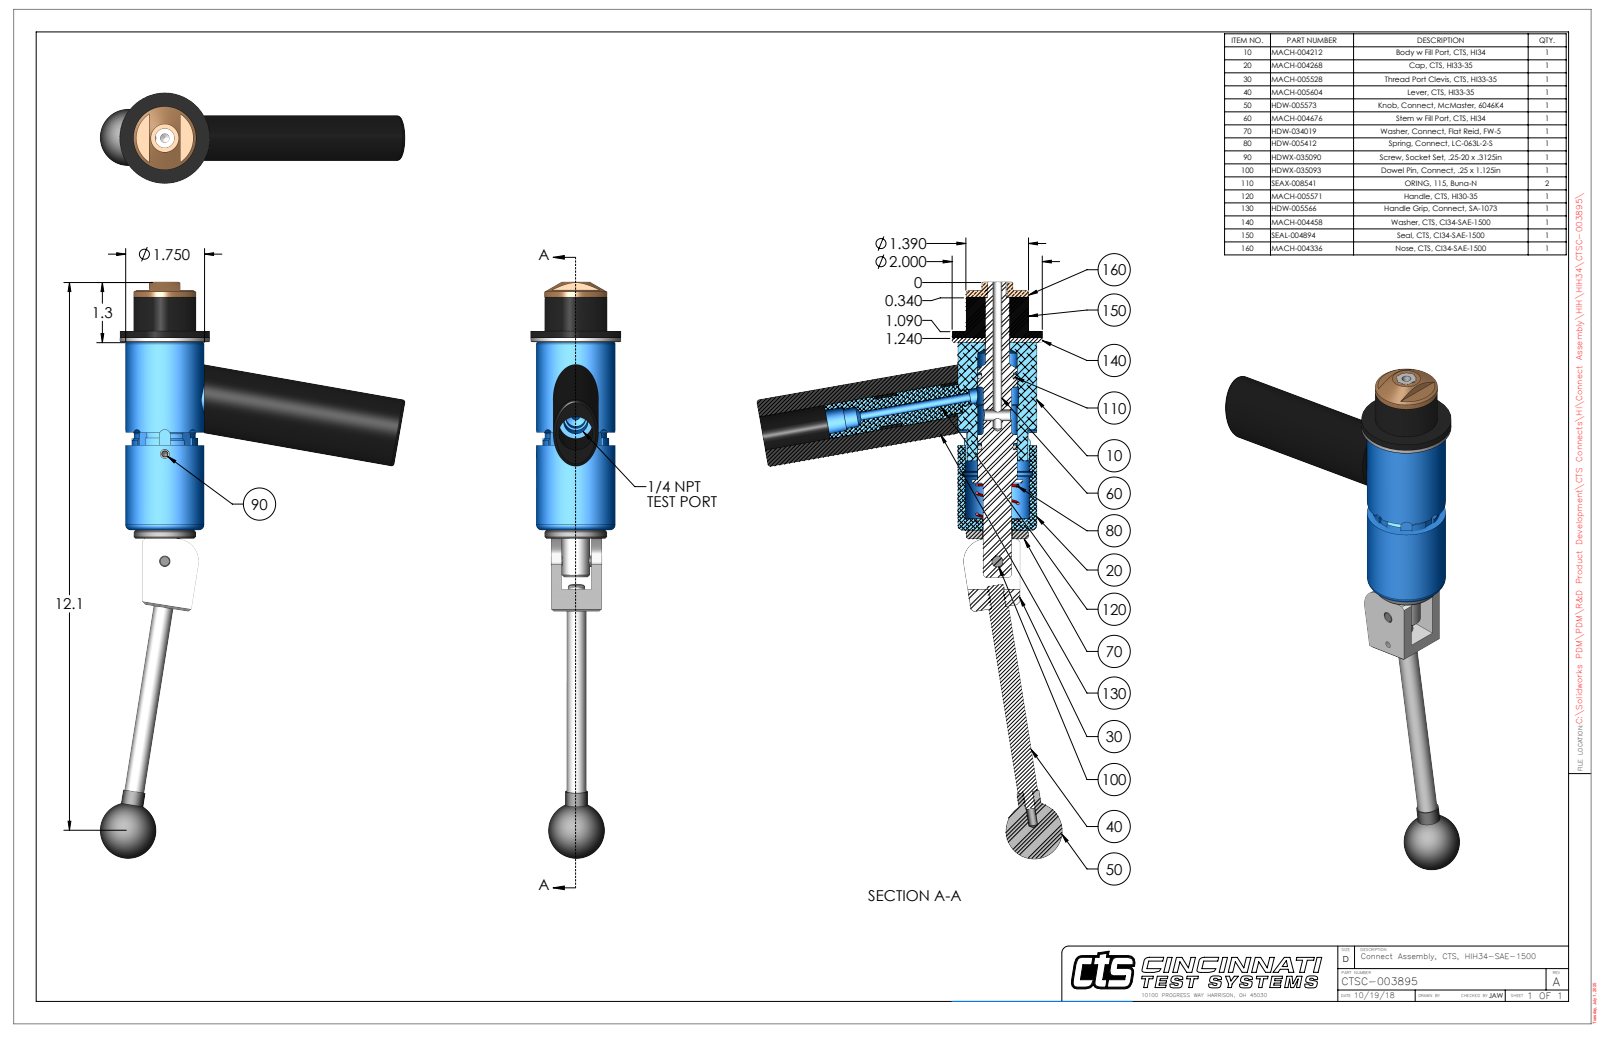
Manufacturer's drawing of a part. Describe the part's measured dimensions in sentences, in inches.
The part is named "CTSC-003895". Its 3-D file was written by "SolidWorks 2023 (AUTOMOTIVE_DESIGN)". It is 10 solids with 327 faces: 117 planar, 140 cylindrical and 70 other. Overall it measures 12.773 by 6.763 by 2 inches. Its volume is 19.51 cubic inches and its surface area 125.8 square inches. Round holes: 2 of diameter 0.201, 1 of diameter 0.15, 1 of diameter 0.187, 1 of diameter 0.204, 1 of diameter 0.249, 1 of diameter 0.25, 1 of diameter 0.251, 1 of diameter 0.313, 1 of diameter 0.422, 1 of diameter 0.438, 1 of diameter 0.53, 1 of diameter 0.541. Round bosses or shafts: 2 of diameter 0.5, 2 of diameter 0.44, 2 of diameter 0.25, 1 of diameter 2, 1 of diameter 1.75, 1 of diameter 1.39, 1 of diameter 1.38, 1 of diameter 0.75. Partial cylindrical surfaces (rounded edges, fillets, slot ends): 4 of radius 0.125, 2 of radius 0.029, 1 of radius 0.166, 1 of radius 0.166, 1 of radius 0.186, 1 of radius 0.33, 1 of radius 0.5, 1 of radius 0.709. The main face-to-face distances are 0.094, 0.9, 0.994, 5.158, 4.258, 4.164, 1.12, 0.75, 0.15, 0.244. The hole center spacings are 0.74, 2.376, 3.116.
